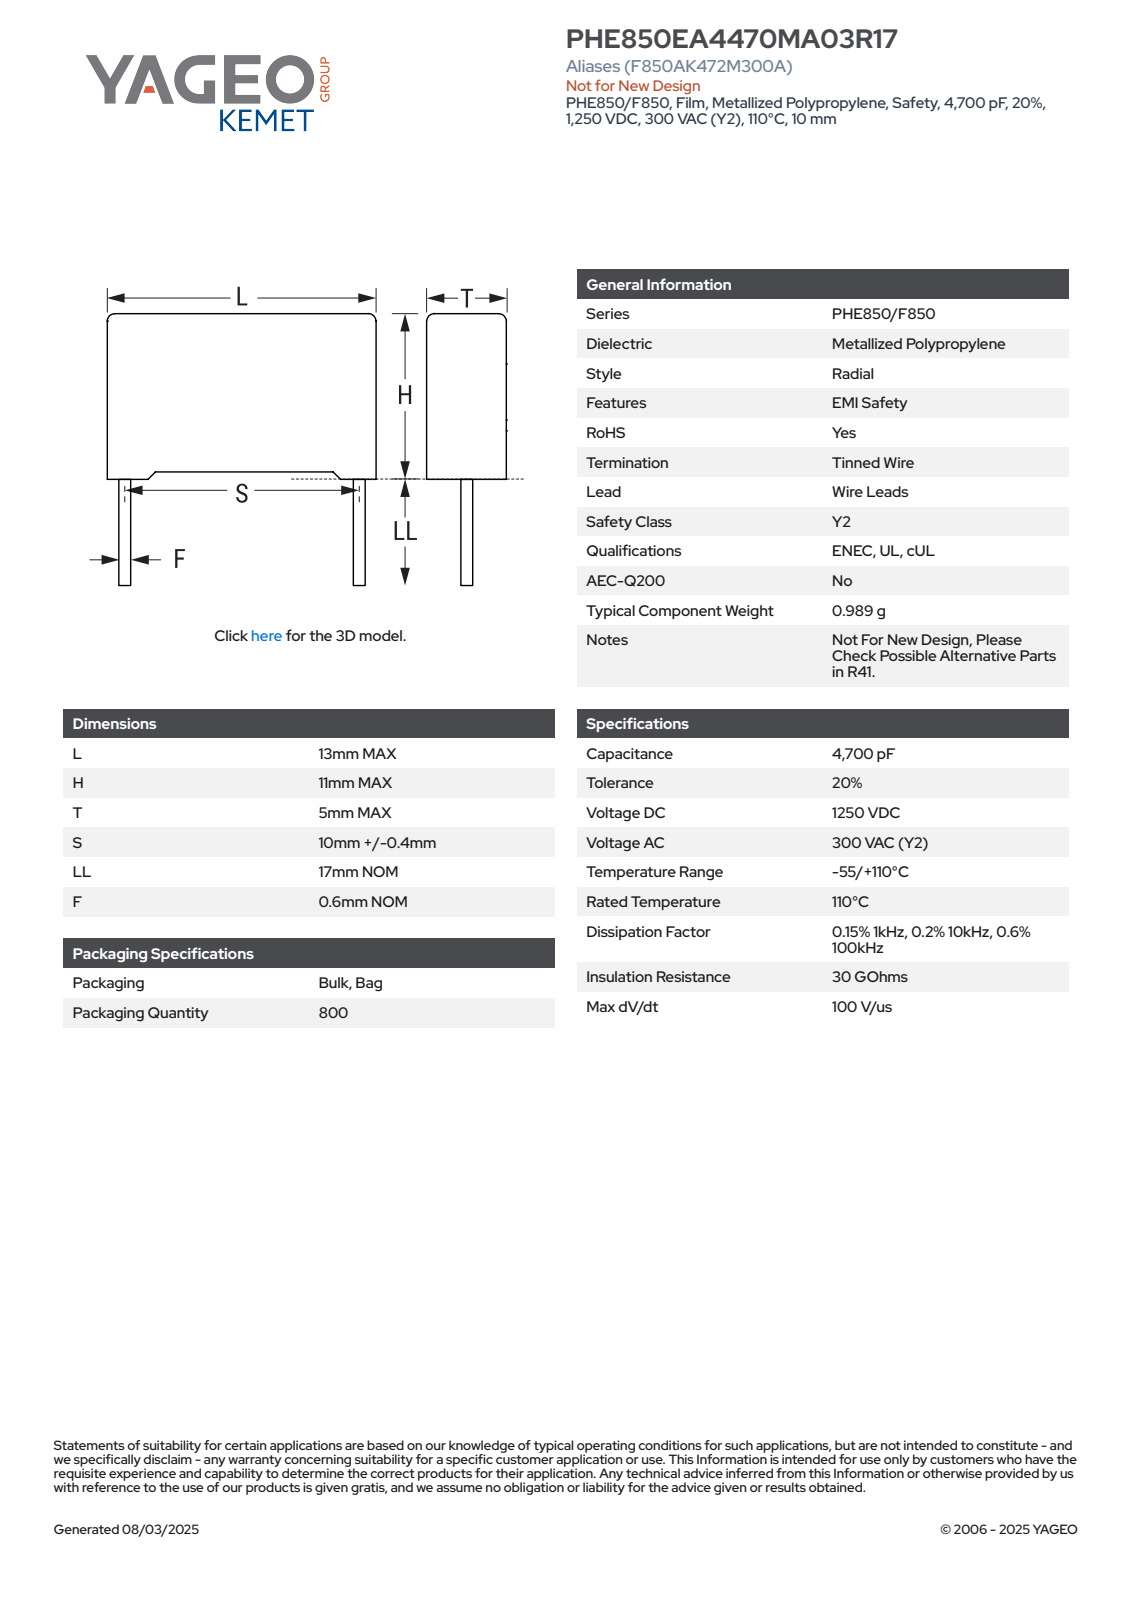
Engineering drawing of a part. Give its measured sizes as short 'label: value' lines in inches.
name: CFR_RB2_13X11X5_L13H11T5S10LL17F0.6
written by: SolidWorks 2021 (AUTOMOTIVE_DESIGN)
unit: in
bodies: 4 solids, 85 faces (77 planar, 8 cylindrical, 0 other)
size: 1.102 × 0.512 × 0.197
volume: 0.042 in³; area: 0.949 in²
bosses: 2× ⌀0.024
rounds: 4× R0.02
face distances: 0.197, 0.512, 0.404, 0.017, 0.18, 0.03, 0.433, 0.163, 0.495, 0.015
